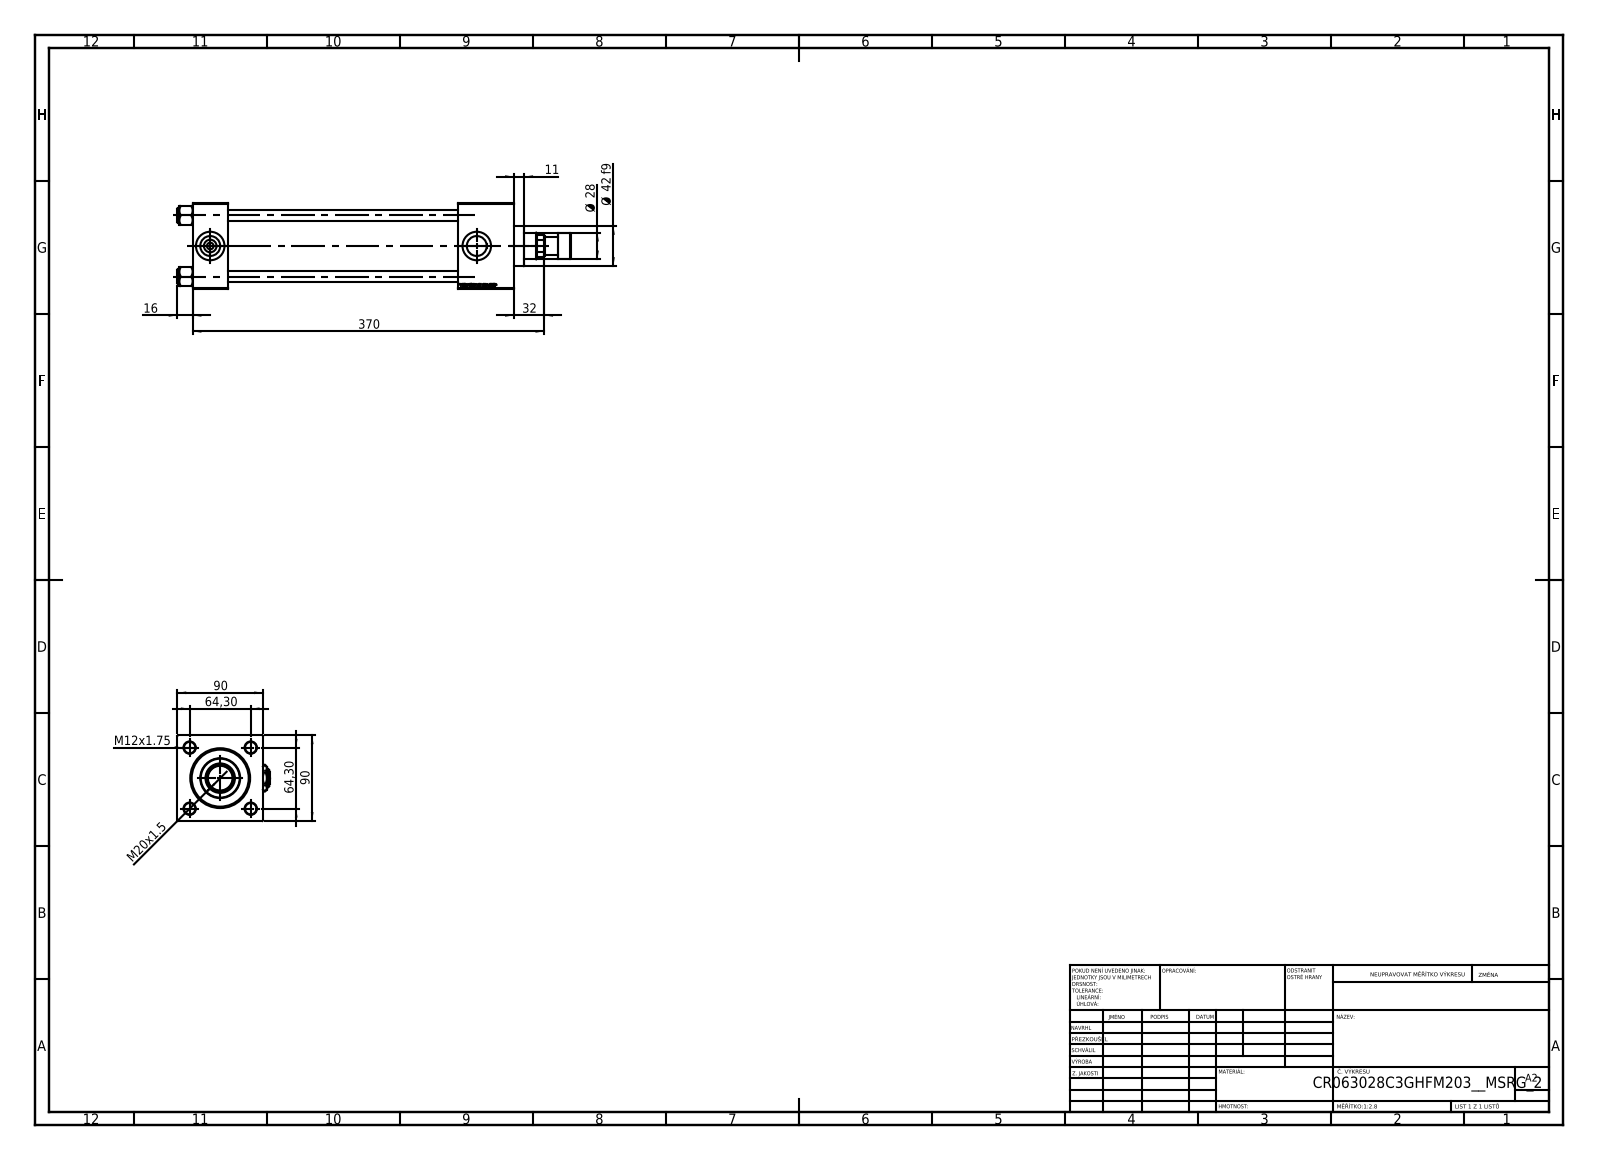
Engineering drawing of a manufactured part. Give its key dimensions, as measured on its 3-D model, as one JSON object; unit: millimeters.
{"part_name": "V215CR_VCP_C; NUT_M5_C; V215CR_C_TYCINKA; V215_VC_A (+3 more)", "step_written_by": "SolidWorks 2019 (CONFIG_CONTROL_DESIGN)", "units": "millimeters", "bodies": {"solids": 14, "faces": 1264, "planar": 578, "cylindrical": 102, "other": 584}, "overall_size": [414, 97, 90], "volume_mm3": 1261000, "surface_area_mm2": 306754, "round_holes": [[12, 4], [7, 2], [20.96, 2], [30, 2], [18.5, 1], [28, 1], [31, 1], [50, 1], [60, 1], [63, 1]], "round_bosses_or_shafts": [[15, 4], [69, 1], [42, 1], [27, 1], [18, 1]], "face_to_face_distances": [90, 37, 301, 338, 59, 279, 242, 309.3, 272.3, 30.3], "hole_center_spacings": [45.47, 64.3, 90.93, 280.5]}
